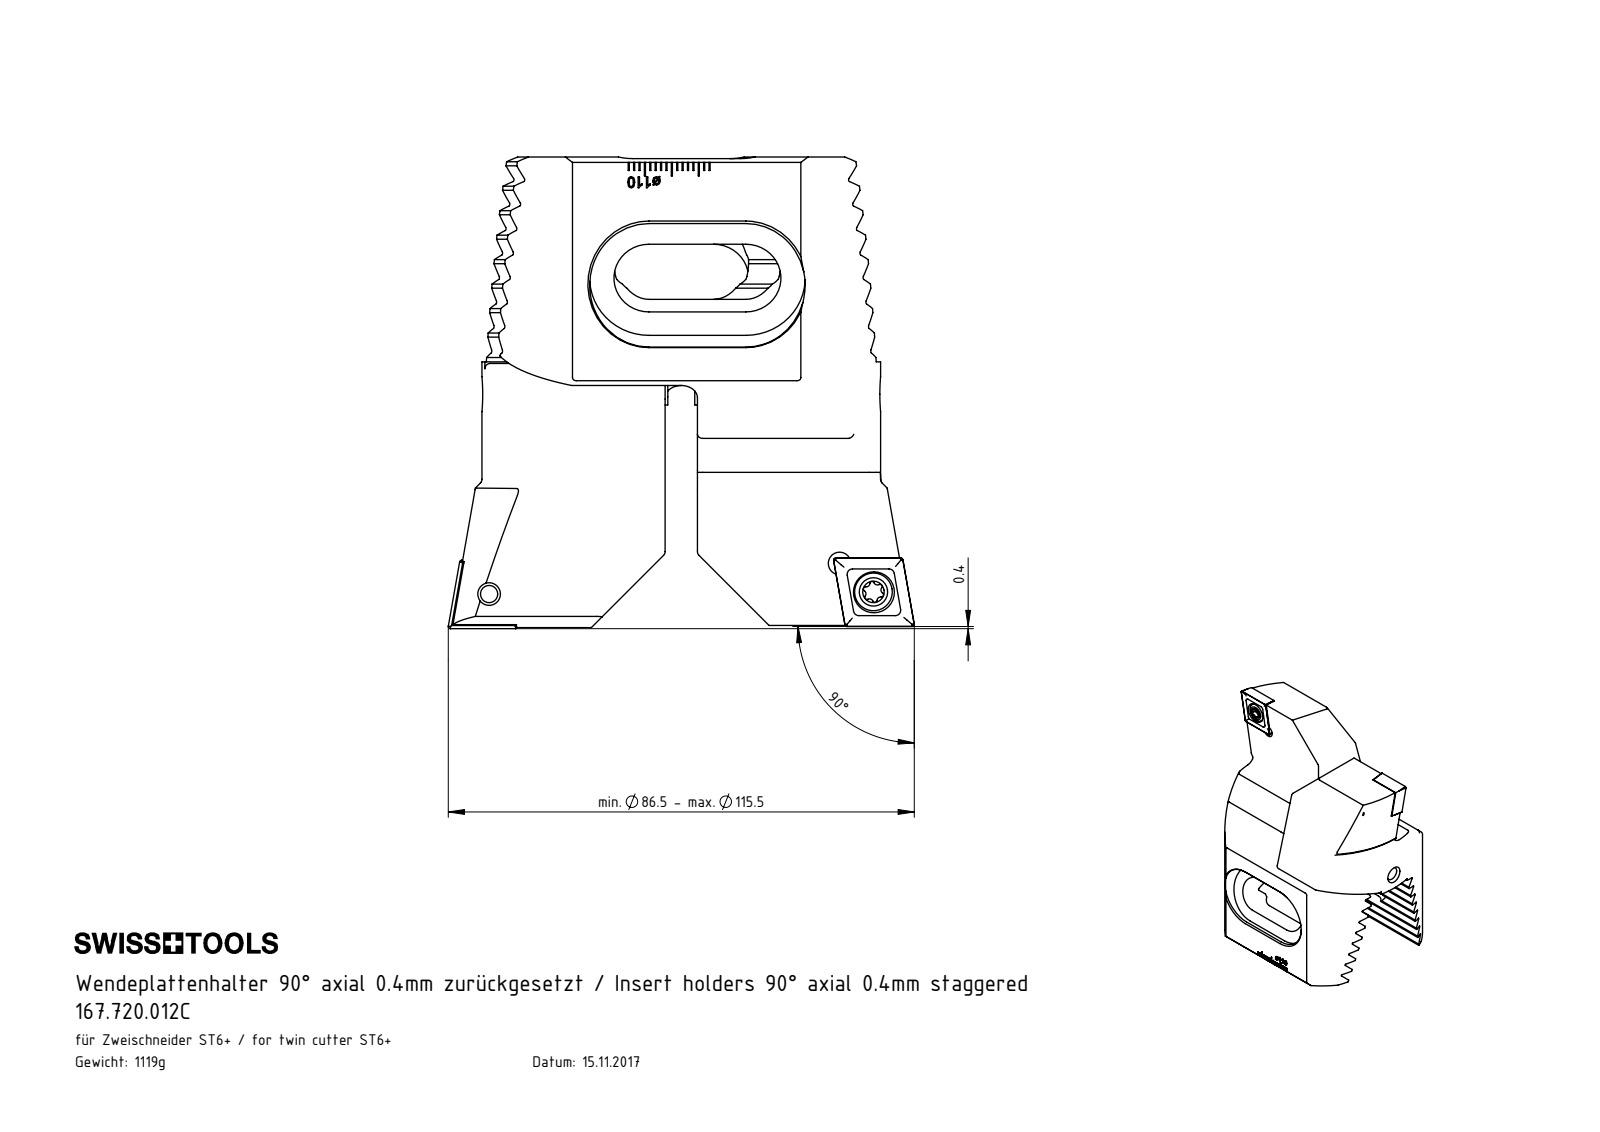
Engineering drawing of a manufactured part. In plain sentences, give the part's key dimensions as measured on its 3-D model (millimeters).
The part is named "ISO 4028 - M3 x 5_M3x8; 167.720.012C; Z72-ER3.001.030; ZC7-xxx.001.050_A (+3 more)". Its 3-D file was written by "SolidWorks 2017 (CONFIG_CONTROL_DESIGN)". It is 8 solids with 746 faces: 411 planar, 143 cylindrical and 192 other. Overall it measures 87.5 by 86.5 by 58.2 millimeters. Its volume is 142 276 cubic millimeters and its surface area 37 228 square millimeters. Round holes: 4 of diameter 4.2, 2 of diameter 5, 2 of diameter 5.5, 2 of diameter 7.6, 1 of diameter 2, 1 of diameter 2.5, 1 of diameter 8. Round bosses or shafts: 2 of diameter 7, 2 of diameter 5, 1 of diameter 6, 1 of diameter 4, 1 of diameter 3, 1 of diameter 2. Partial cylindrical surfaces (rounded edges, fillets, slot ends): 16 of radius 0.34, 16 of radius 1, 12 of radius 0.39, 6 of radius 0.69, 6 of radius 0.69, 4 of radius 3, 4 of radius 6.5, 4 of radius 11. The main face-to-face distances are 4.07, 8.14, 20.36, 12.21, 28.8, 29.4, 58.2, 16.29, 20.34, 24.43. The hole center spacings are 8.21, 8.33, 71.43, 20, 58.76, 65.23, 65.3, 65.33.
